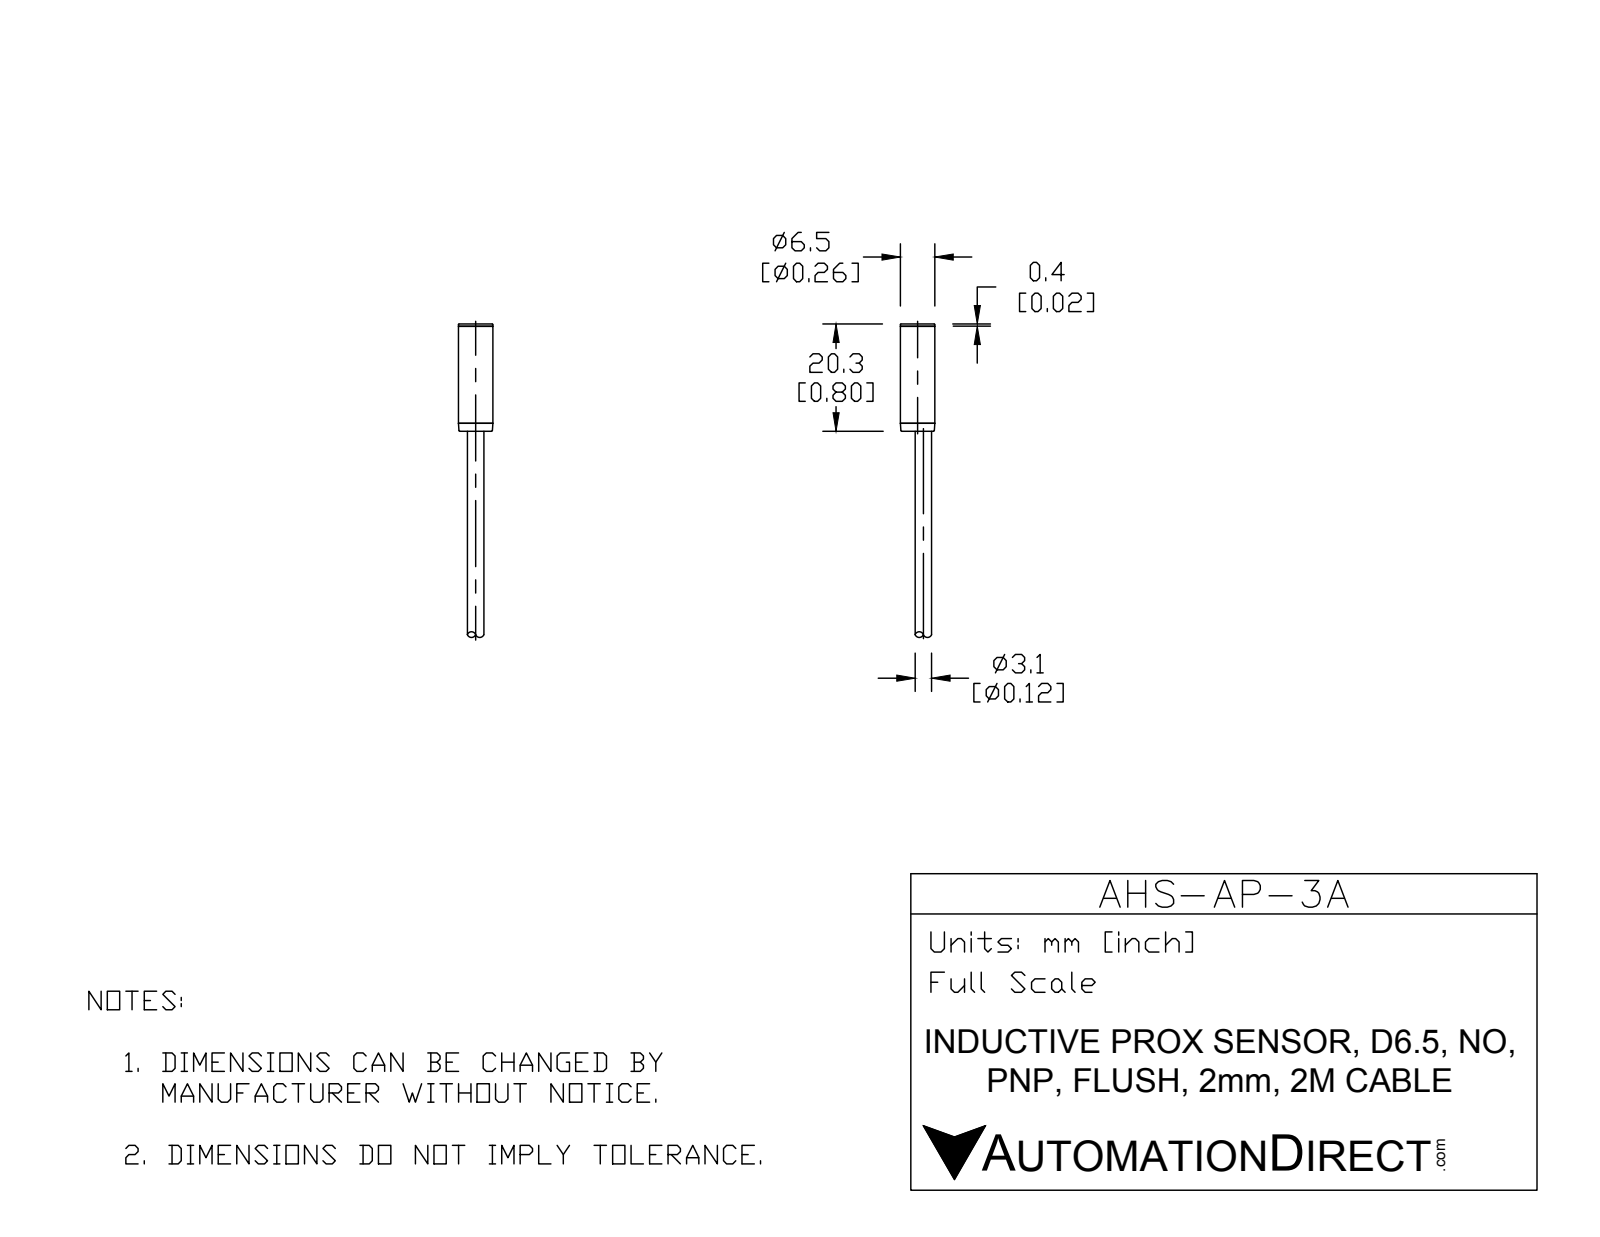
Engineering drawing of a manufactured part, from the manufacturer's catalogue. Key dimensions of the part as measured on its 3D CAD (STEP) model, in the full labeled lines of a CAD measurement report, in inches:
Part name (STEP PRODUCT): AHS-AP-3A
STEP written by: SolidWorks 2015 (CONFIG_CONTROL_DESIGN)
Units: inches
Bodies: 2 solids, 17 faces (5 planar, 6 cylindrical, 6 other)
Overall size (bounding box): 2.768 × 0.256 × 0.256
Volume: 0.064 in³ · Surface area: 1.52 in²
Round bosses / shafts (diameter × count): ⌀0.256 ×1, ⌀0.122 ×1
Main face-to-face distances: 0.799, 1.969, 2.768, 2.752, 0.783, 0.016
